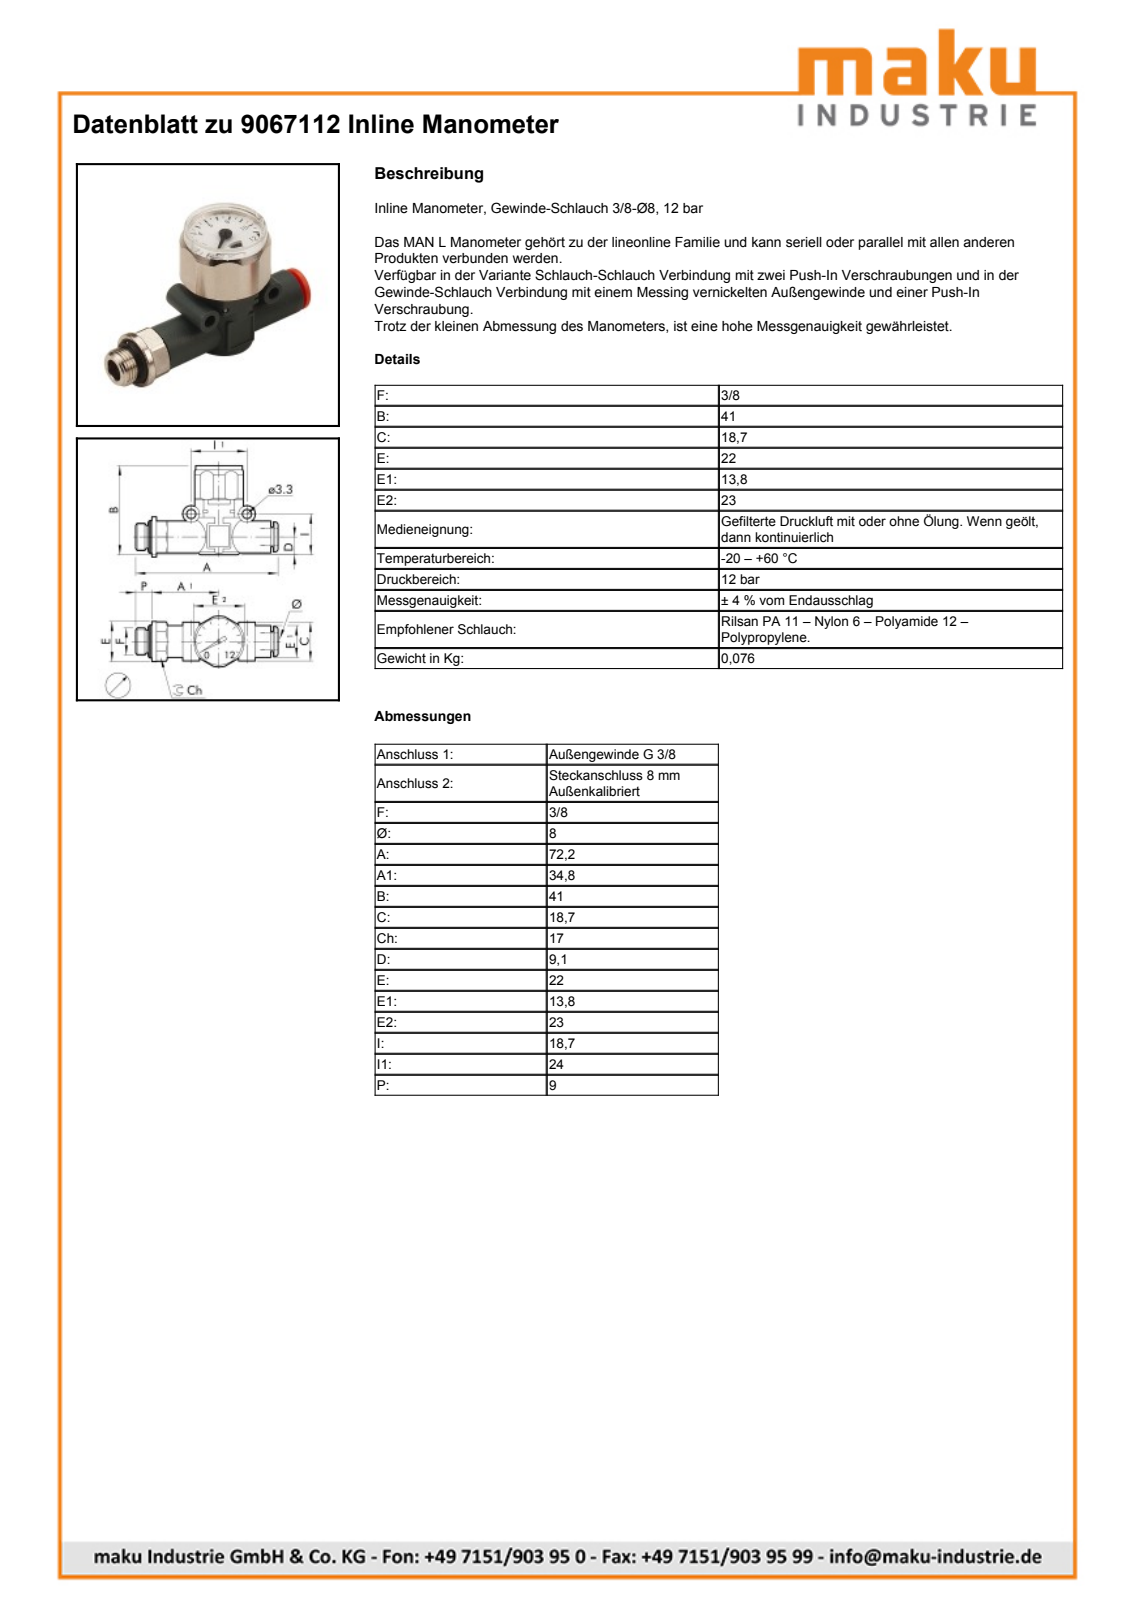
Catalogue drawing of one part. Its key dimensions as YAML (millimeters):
part_name: "9067112; LINE-ON-LINE D8 V2v/V3V_L body; LINE-ON-LINE D8 VNR-L bushing; LINE-ON-LINE D8-3/8 MAN-L thread port (+1 more)"
step_written_by: "PARTsolutions (AUTOMOTIVE_DESIGN)"
units: millimeters
bodies: {solids: 4, faces: 215, planar: 138, cylindrical: 60, other: 17}
overall_size: [72.4, 43, 22]
volume: 17432
surface_area: 11843
round_holes:
  - {diameter: 3.3, count: 2}
  - {diameter: 6, count: 2}
  - {diameter: 5.5, count: 1}
  - {diameter: 8.1, count: 1}
  - {diameter: 10, count: 1}
  - {diameter: 11, count: 1}
  - {diameter: 11.65, count: 1}
  - {diameter: 12.5, count: 1}
  - {diameter: 15, count: 1}
  - {diameter: 17.61, count: 1}
  - {diameter: 18.86, count: 1}
round_bosses_or_shafts:
  - {diameter: 6, count: 2}
  - {diameter: 22, count: 1}
  - {diameter: 20.96, count: 1}
  - {diameter: 18.8, count: 1}
  - {diameter: 17.91, count: 1}
  - {diameter: 16.66, count: 1}
  - {diameter: 14.6, count: 1}
  - {diameter: 13.8, count: 1}
partial_cylinders:
  - {radius: 0.71, count: 1}
  - {radius: 3.75, count: 1}
  - {radius: 9.6, count: 1}
  - {radius: 10.2, count: 1}
  - {radius: 10.35, count: 1}
  - {radius: 11.45, count: 1}
  - {radius: 11.5, count: 1}
face_to_face_distances: [0.75, 20, 16.62, 22, 21.25, 2, 24.1, 40.72, 17, 11.8]
hole_center_spacings: [15.37, 24]
